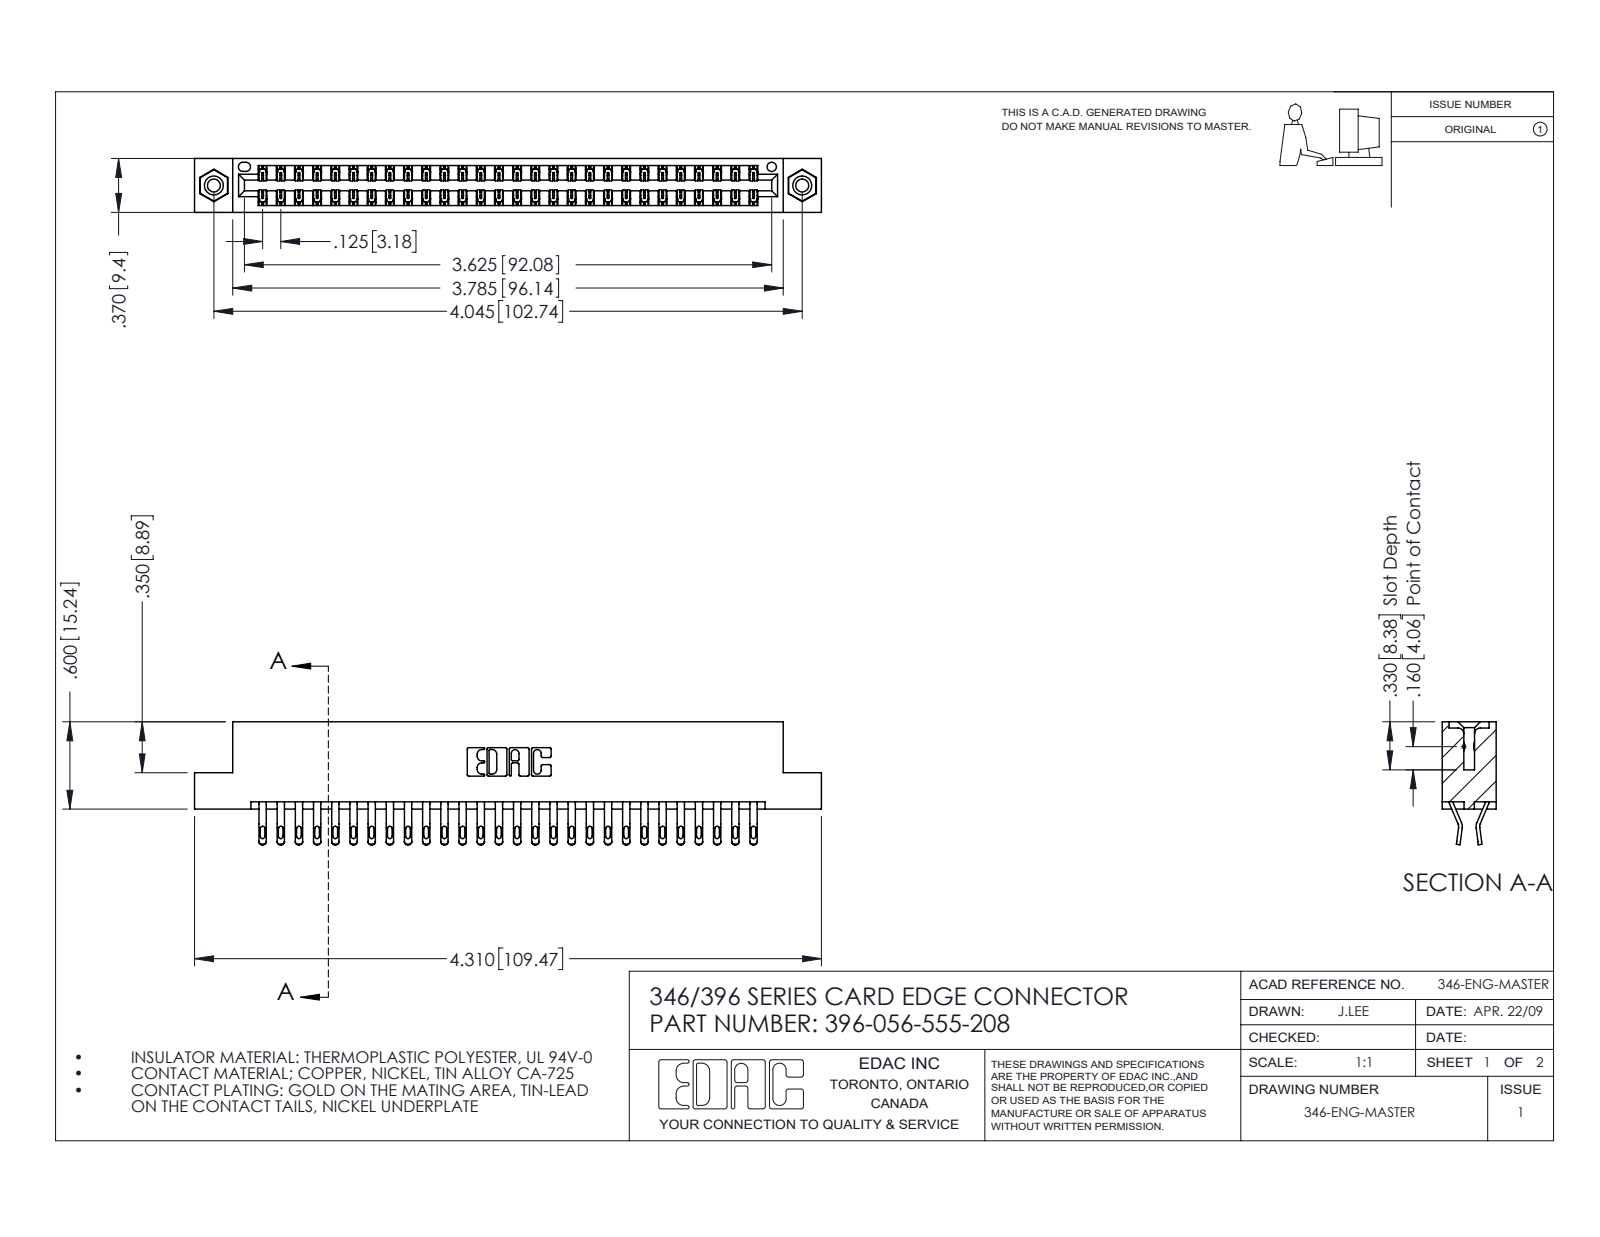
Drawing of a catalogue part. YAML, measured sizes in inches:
part_name: "345-250-001_345-250-003-102; 396-056-555-208; 346 Part_Flush Mounting Lugs - 0.156 Dia-TI; 345-292-001_555 Tail"
step_written_by: "SolidWorks 2016 (CONFIG_CONTROL_DESIGN)"
units: inches
bodies: {solids: 59, faces: 3430, planar: 1956, cylindrical: 1458, other: 16}
overall_size: [4.31, 0.845, 0.37]
volume: 0.654
surface_area: 23.43
round_holes:
  - {diameter: 0.089, count: 2}
  - {diameter: 0.125, count: 2}
  - {diameter: 0.156, count: 2}
  - {diameter: 0.064, count: 1}
round_bosses_or_shafts:
  - {diameter: 0.155, count: 2}
partial_cylinders:
  - {radius: 0.016, count: 112}
  - {radius: 0.02, count: 112}
  - {radius: 0.006, count: 84}
  - {radius: 0.01, count: 22}
  - {radius: 0.007, count: 6}
  - {radius: 0.031, count: 6}
  - {radius: 0.026, count: 3}
  - {radius: 0.01, count: 2}
face_to_face_distances: [0.048, 0.322, 0.37, 0.25, 0.025, 0.072, 0.298, 0.275, 0.148, 0.222]
hole_center_spacings: [0.246, 3.837, 4.045]
